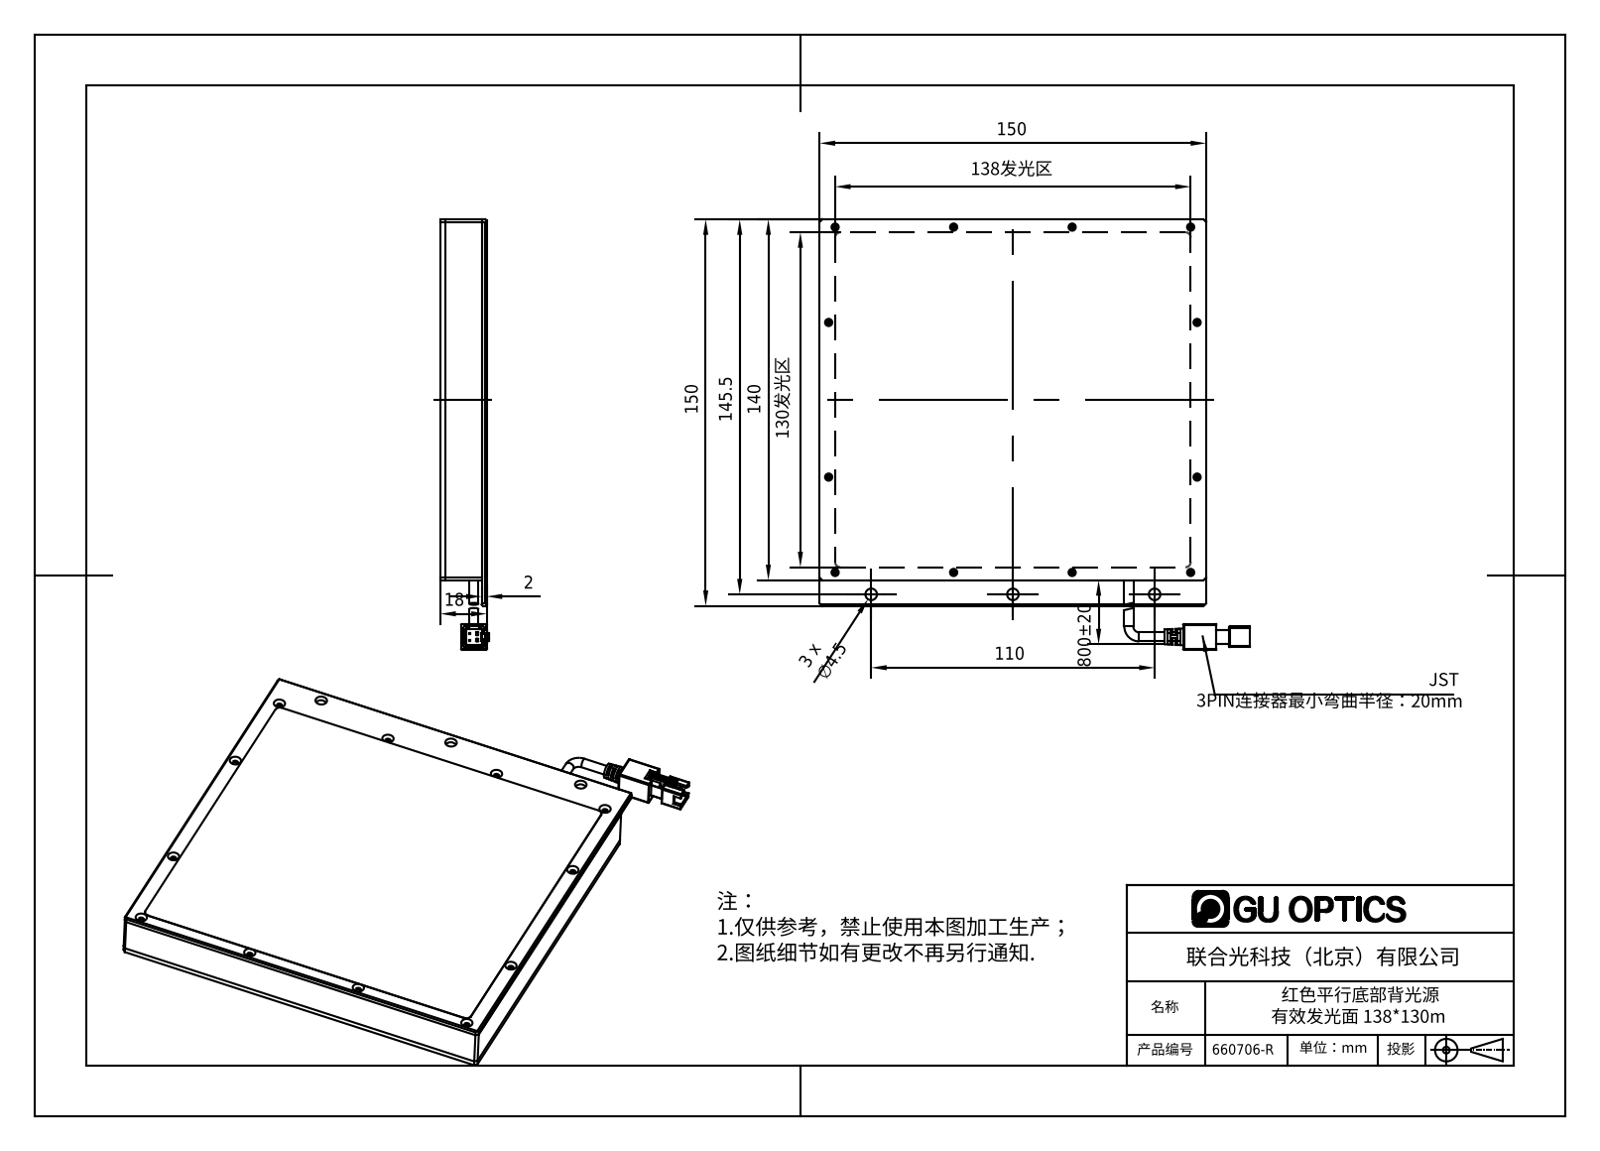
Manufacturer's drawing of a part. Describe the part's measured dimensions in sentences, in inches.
The part is named "660706-R". Its 3-D file was written by "SolidWorks 2016 (AUTOMOTIVE_DESIGN)". It is 22 solids with 3025 faces: 2614 planar, 253 cylindrical and 158 other. Overall it measures 6.575 by 6.575 by 0.736 inches. Its volume is 10.54 cubic inches and its surface area 244.2 square inches. Round holes: 12 of diameter 0.043, 12 of diameter 0.055, 12 of diameter 0.059, 12 of diameter 0.063, 12 of diameter 0.079, 12 of diameter 0.087, 12 of diameter 0.11, 3 of diameter 0.177. Round bosses or shafts: 2 of diameter 0.138. Partial cylindrical surfaces (rounded edges, fillets, slot ends): 15 of radius 0.004, 13 of radius 0.008, 12 of radius 0.016, 4 of radius 0.039, 4 of radius 0.079, 2 of radius 0.059, 1 of radius 0.012, 1 of radius 0.027. The main face-to-face distances are 0.079, 0.551, 0.63, 0.083, 0.634, 0.713, 0.472, 0.161, 0.197, 0.039. The hole center spacings are 1.811, 5.578, 1.46, 2.402, 3.622, 3.82, 3.996, 4.27.
